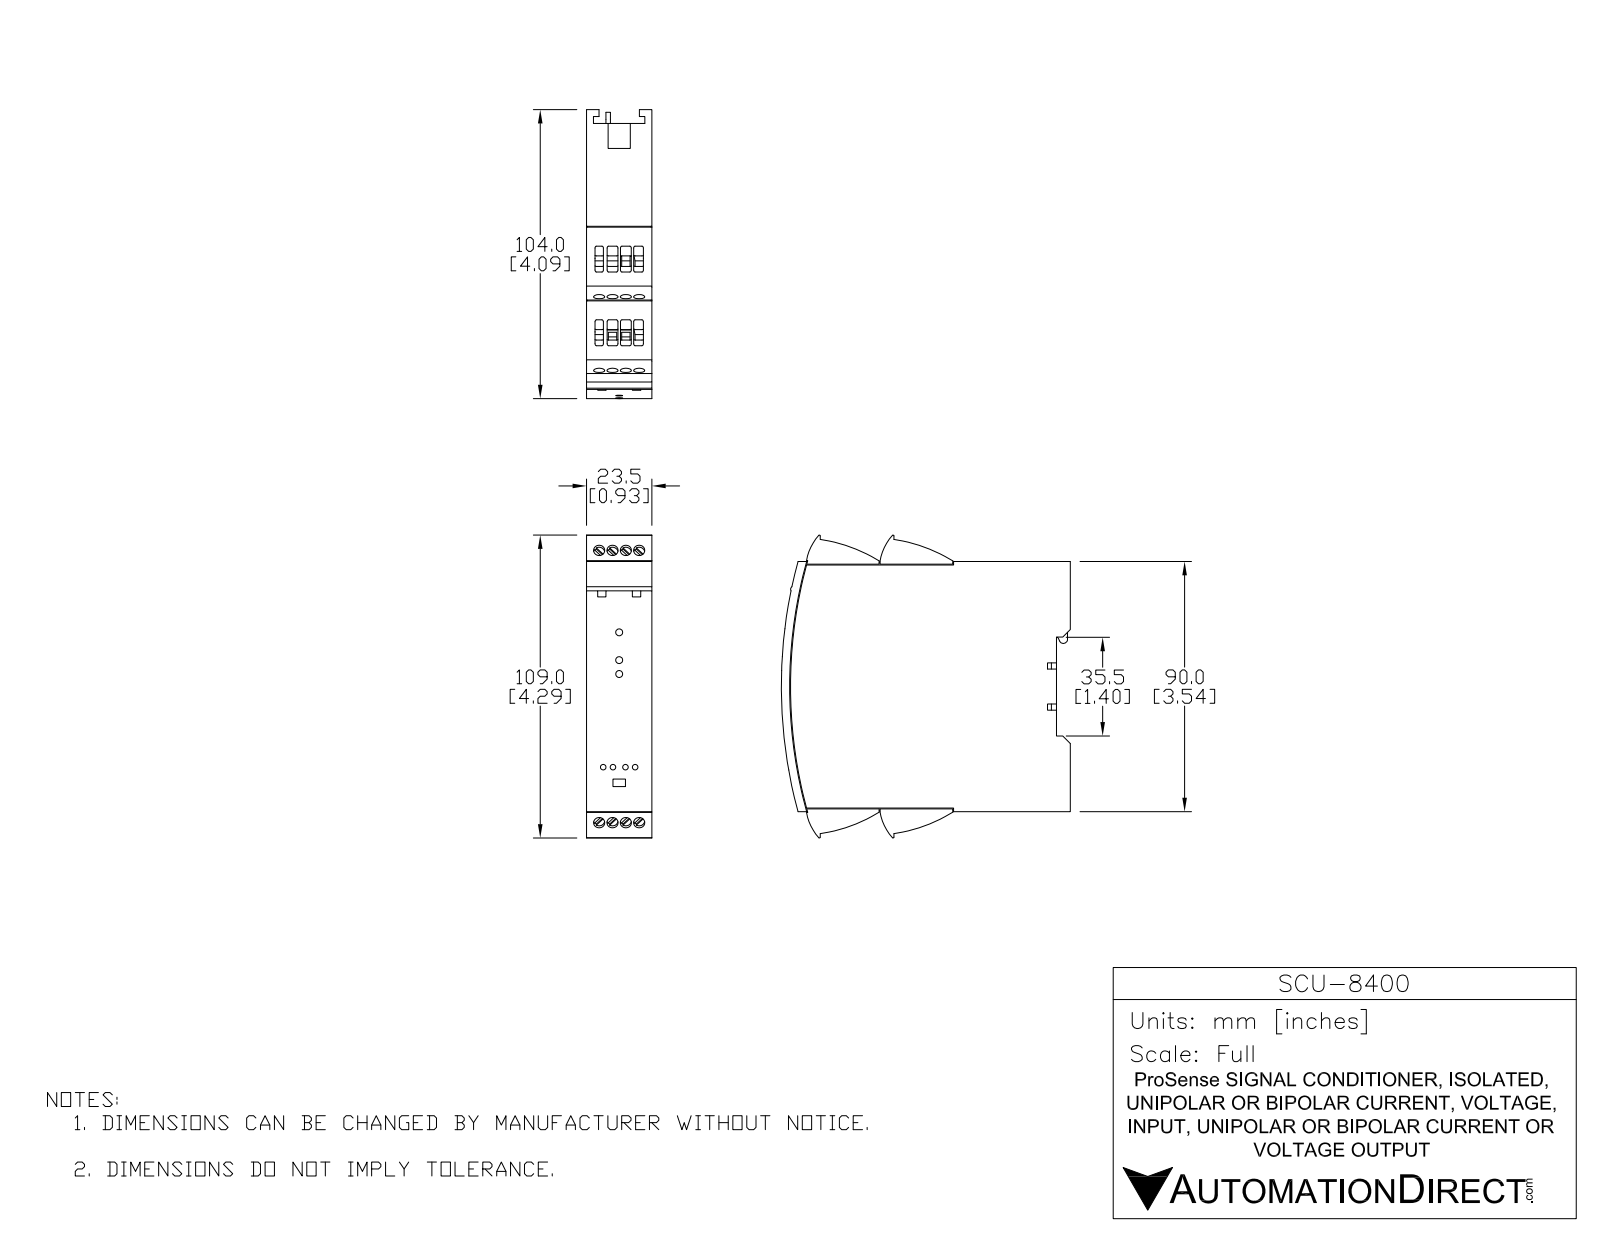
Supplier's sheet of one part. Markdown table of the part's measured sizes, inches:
| quantity | value |
| --- | --- |
| part name | SCU-8400 |
| STEP written by | SolidWorks 2017 (AUTOMOTIVE_DESIGN) |
| units | inches |
| bodies | 1 solid, 1079 faces (626 planar, 211 cylindrical, 242 other) |
| overall size | 4.291 × 4.094 × 0.925 |
| volume | 13.23 in³ |
| surface area | 50.79 in² |
| round holes (diameter × count) | 0.157 × 16, 0.091 × 4, 0.098 × 1 |
| partial cylindrical surfaces (radius × count) | 0.02 × 67, 0.039 × 9, 0.012 × 4, 0.726 × 4, 2.175 × 4, 6.762 × 2, 0.043 × 1, 0.059 × 1 |
| main face-to-face distances | 0.925, 3.543, 0.098, 0.197, 0.189, 0.177, 0.65, 0.12, 0.805, 0.079 |
| hole center spacings | 0.189, 0.434, 0.378, 0.391, 0.544, 0.567, 0.689, 0.209 |
